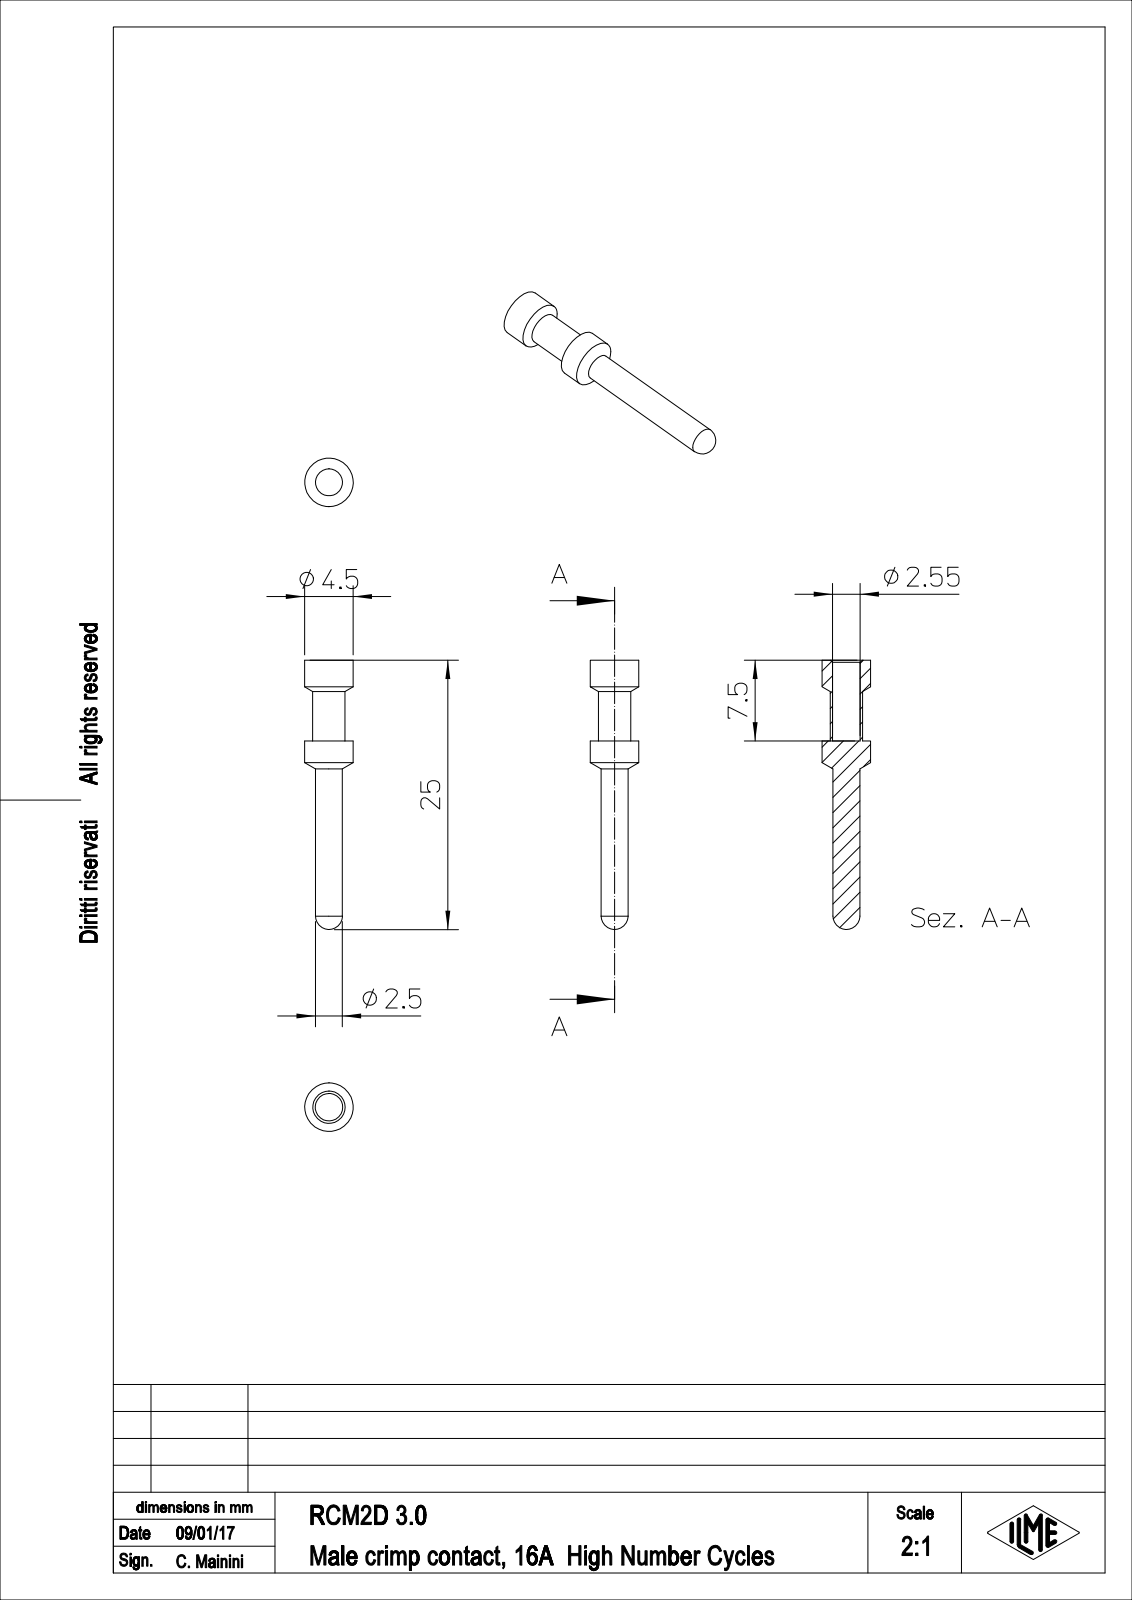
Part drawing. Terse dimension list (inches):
name: RCM2D_3.0
written by: PTC Creo Elements/Direct Modeling 19.0E 27-Jun-2016 (C) Parametric Technology GmbH (AUTOMOTIVE_DESIGN)
unit: in
bodies: 1 solid, 21 faces (3 planar, 10 cylindrical, 8 other)
size: 0.984 × 0.177 × 0.177
volume: 0.009 in³; area: 0.513 in²
holes: 1× ⌀0.1
bosses: 1× ⌀0.177, 1× ⌀0.118, 1× ⌀0.098
face distances: 0.295
